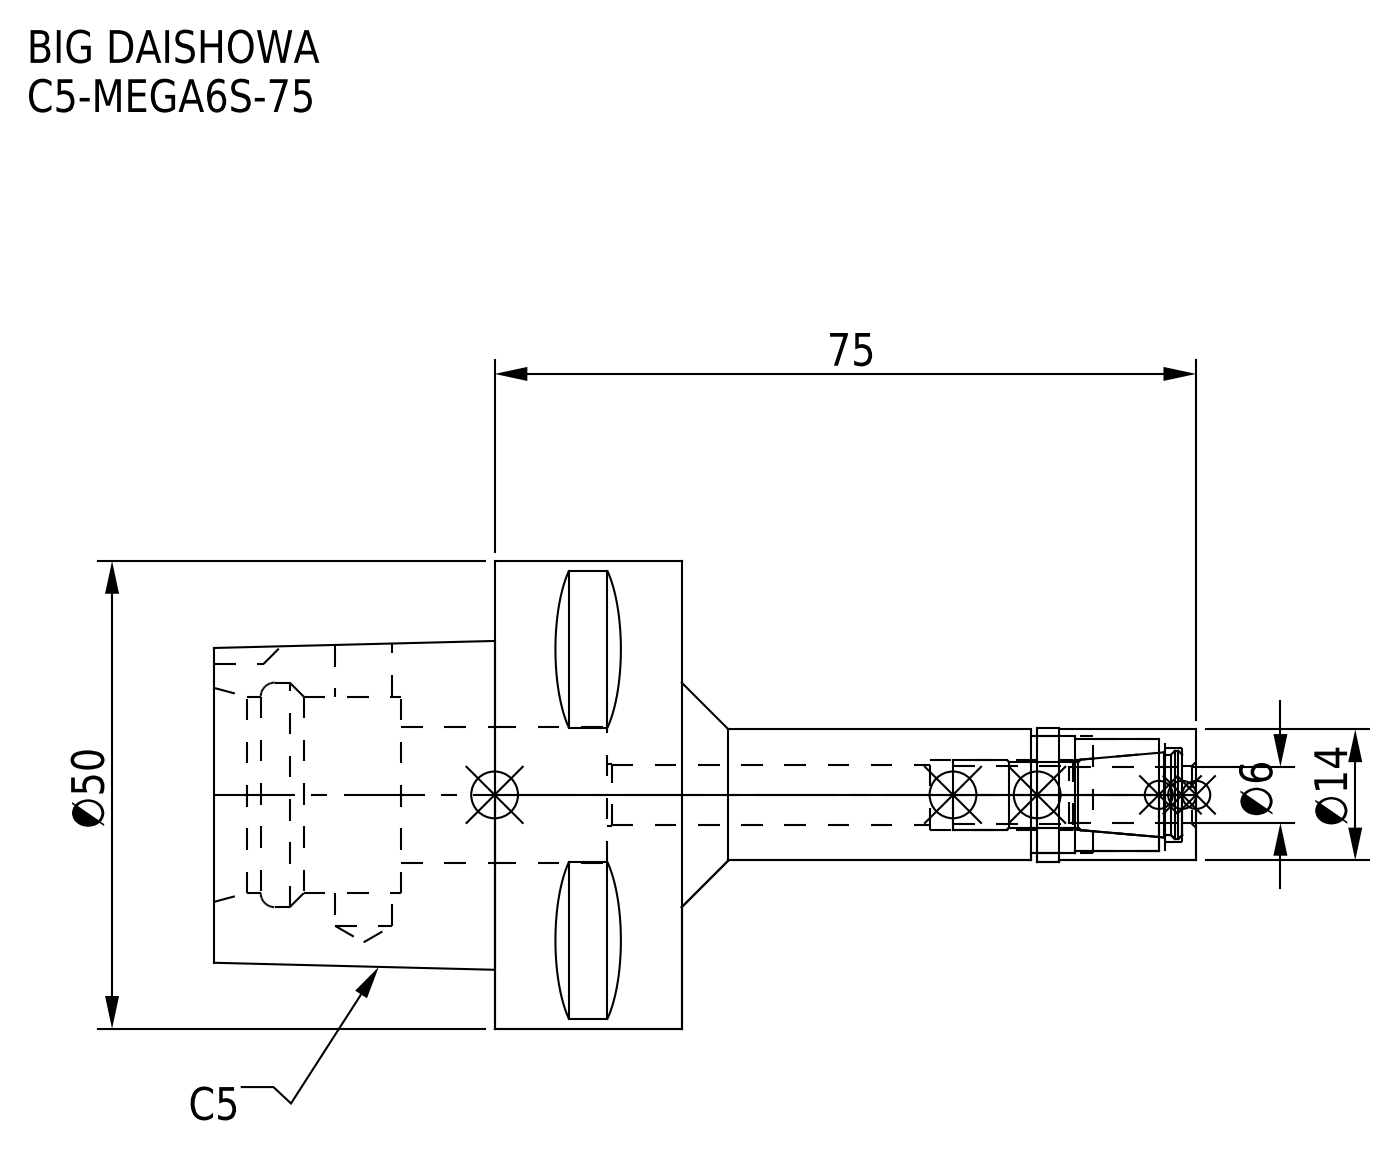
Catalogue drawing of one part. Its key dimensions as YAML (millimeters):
part_name: "C5-MEGA6S-75-060.stp; C5-MEGA6S-75-060_ASM.stp; C5-MEGA6S-75; C5-MEGA6S-75-060-FreeParts (+3 more)"
step_written_by: "SolidWorks 2019 (CONFIG_CONTROL_DESIGN)"
units: millimeters
bodies: {solids: 2, faces: 93, planar: 38, cylindrical: 39, other: 16}
overall_size: [105, 50, 50]
volume: 61091
surface_area: 17861
round_holes:
  - {diameter: 6.1, count: 2}
  - {diameter: 6.4, count: 1}
  - {diameter: 6.6, count: 1}
  - {diameter: 7.4, count: 1}
  - {diameter: 10, count: 1}
  - {diameter: 12, count: 1}
  - {diameter: 12.5, count: 1}
  - {diameter: 14.5, count: 1}
  - {diameter: 21, count: 1}
  - {diameter: 24, count: 1}
round_bosses_or_shafts:
  - {diameter: 50, count: 1}
  - {diameter: 14.3, count: 1}
  - {diameter: 14, count: 1}
partial_cylinders:
  - {radius: 4, count: 1}
face_to_face_distances: [20, 30, 50, 44, 10, 19.18, 42, 8, 12, 22]
